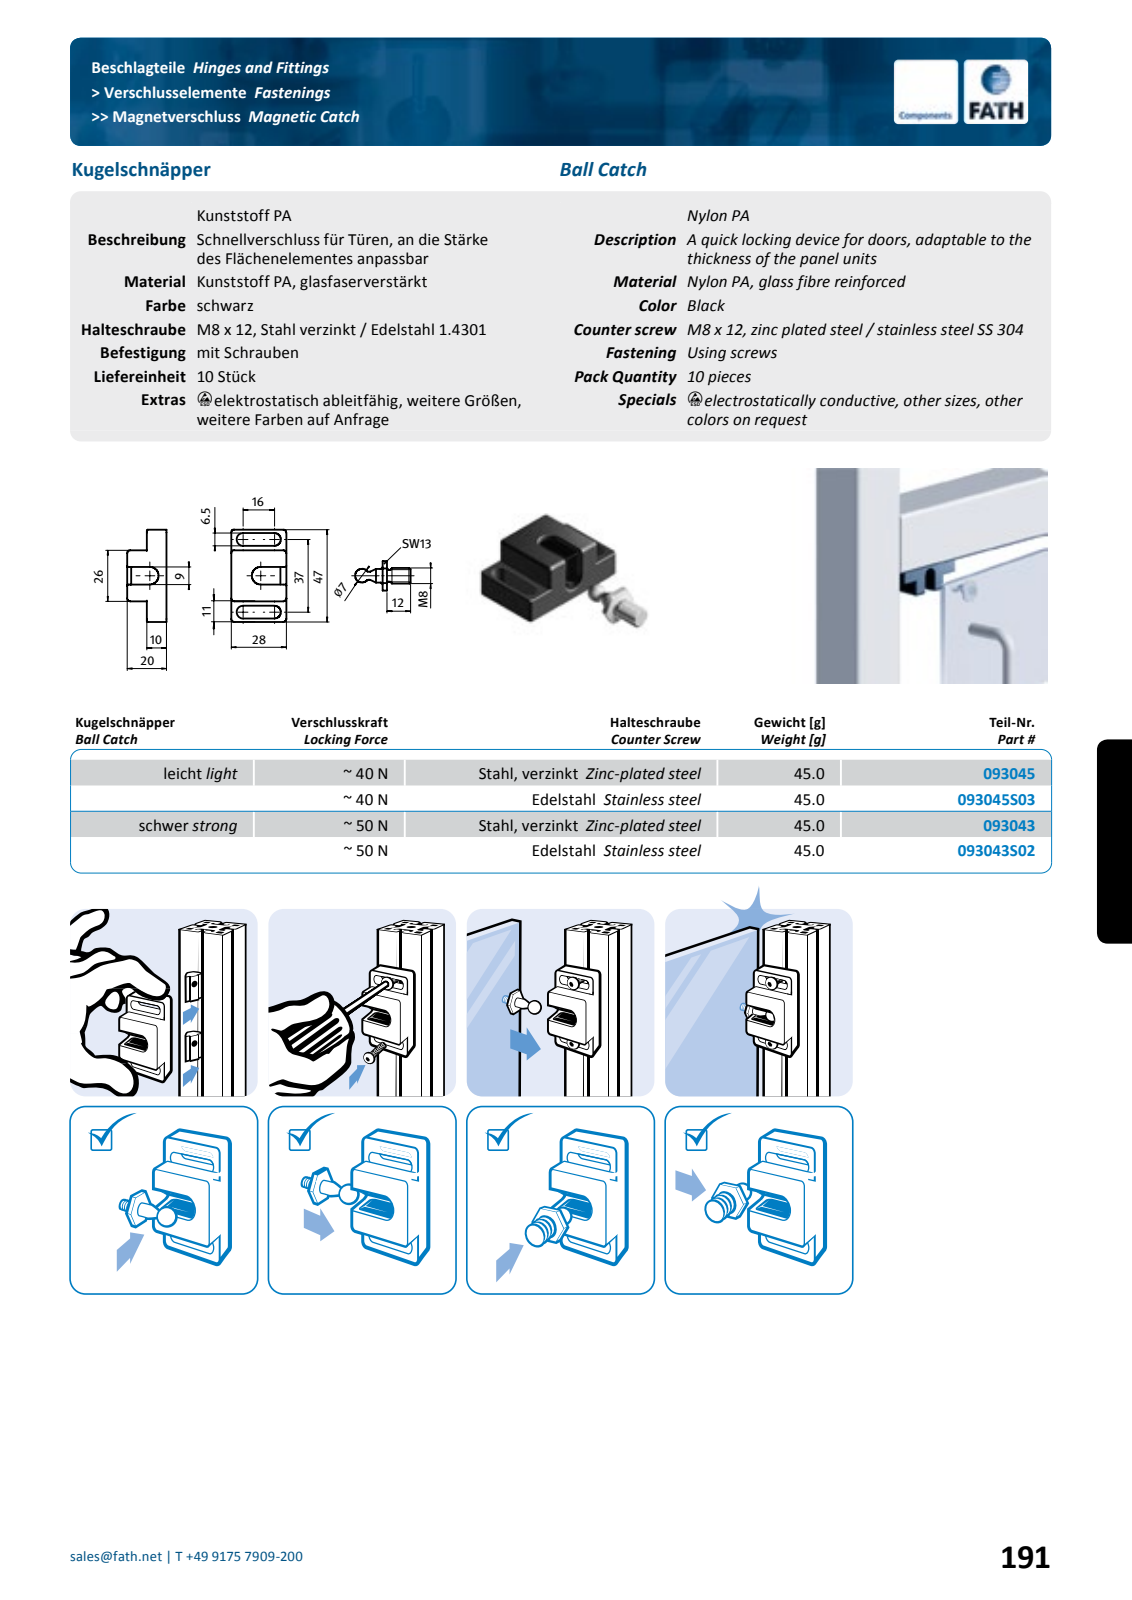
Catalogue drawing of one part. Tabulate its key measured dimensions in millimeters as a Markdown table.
| quantity | value |
| --- | --- |
| part name | fath_093045s03_1; fath_093045s03_2; fath_093045s03_3; fath_093045s03_4 (+3 more) |
| STEP written by | Spatial InterOp 3D (automotive_design) |
| units | millimeters |
| bodies | 7 solids, 476 faces (159 planar, 168 cylindrical, 149 other) |
| overall size | 48 × 34.7 × 28 |
| volume | 12 912 mm³ |
| surface area | 12 355 mm² |
| round holes (diameter × count) | 1.95 × 2 |
| round bosses / shafts (diameter × count) | 7 × 1, 6.35 × 1, 6.2 × 1, 4.7 × 1 |
| partial cylindrical surfaces (radius × count) | 0.2 × 72, 0.5 × 14, 1.5 × 8, 0.4 × 4, 1 × 4, 2 × 4, 3.25 × 4, 3.7 × 4 |
| main face-to-face distances | 2, 24, 8.75, 2.25, 37, 8.5, 10, 4.25, 22, 26 |
| hole center spacings | 20 |
